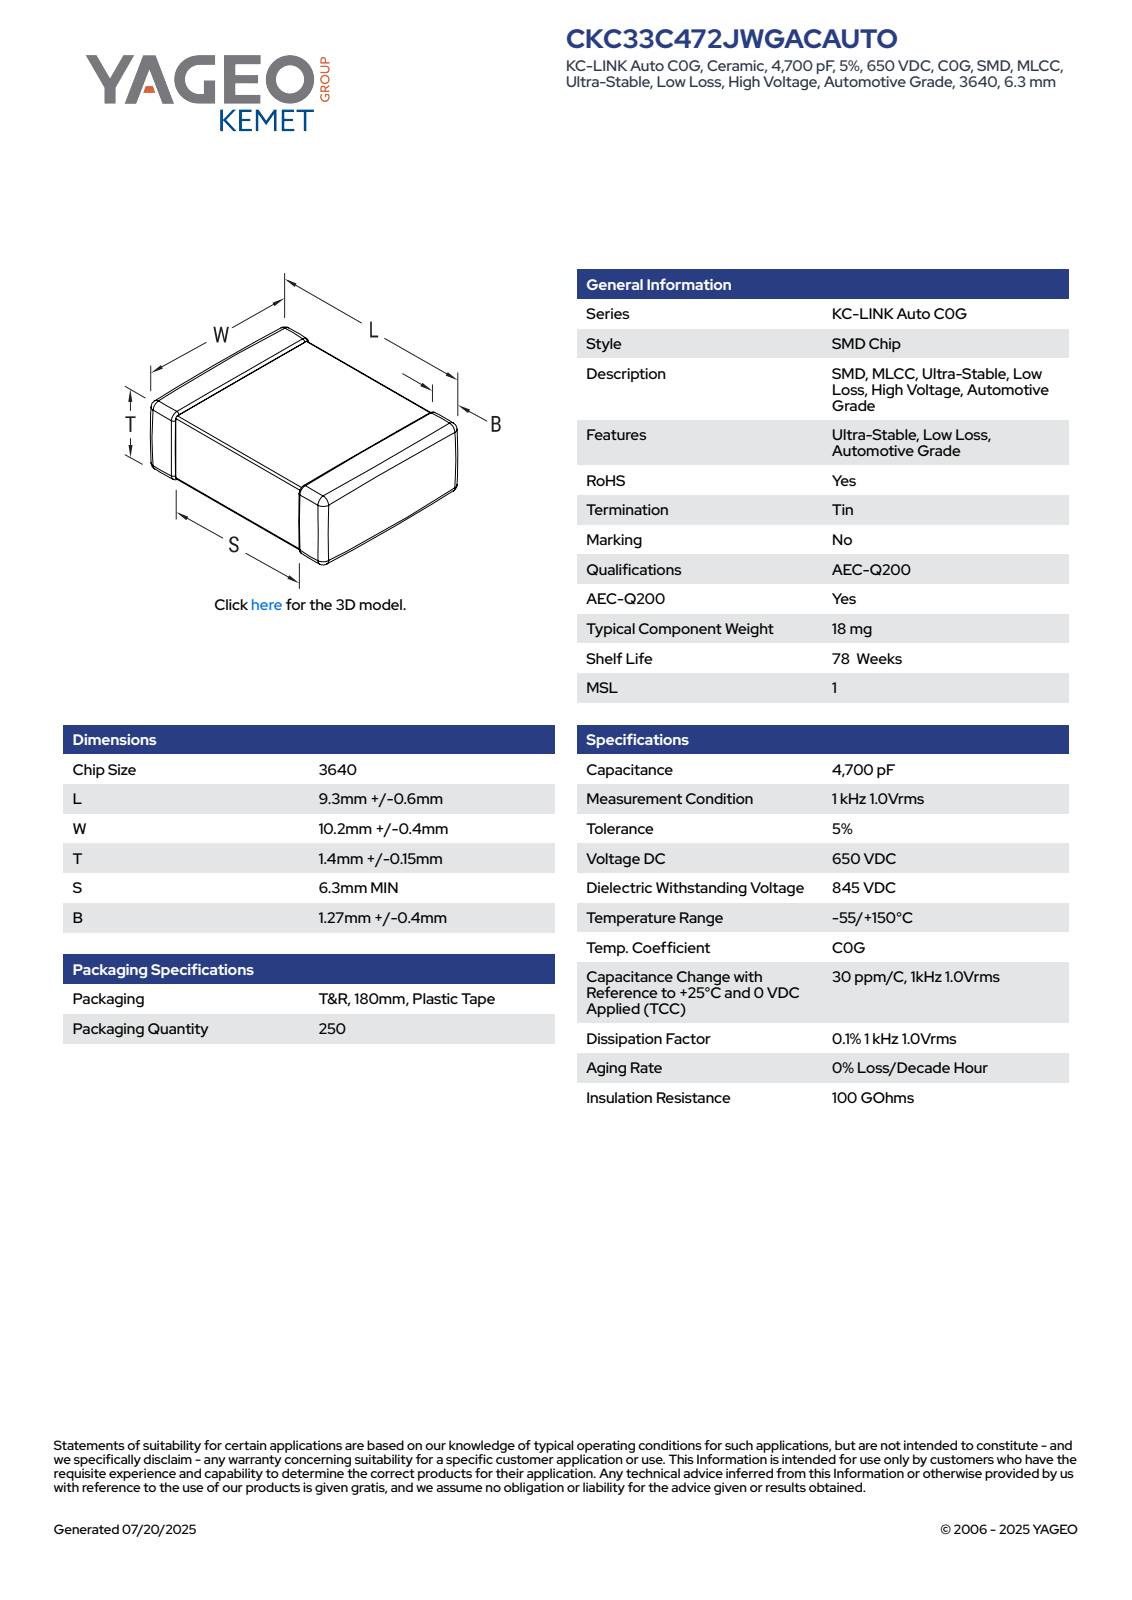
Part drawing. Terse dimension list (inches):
name: CCS_CCSTD_3640_L9.9W10.6T1.55B1.27
written by: SolidWorks 2021 (AUTOMOTIVE_DESIGN)
unit: in
bodies: 4 solids, 125 faces (71 planar, 38 cylindrical, 16 other)
size: 0.417 × 0.39 × 0.061
volume: 0.008 in³; area: 0.425 in²
rounds: 24× R0.009
face distances: 0.044, 0.052, 0.061, 0.39, 0.409, 0.4, 0.417, 0.149, 0.241, 0.211
